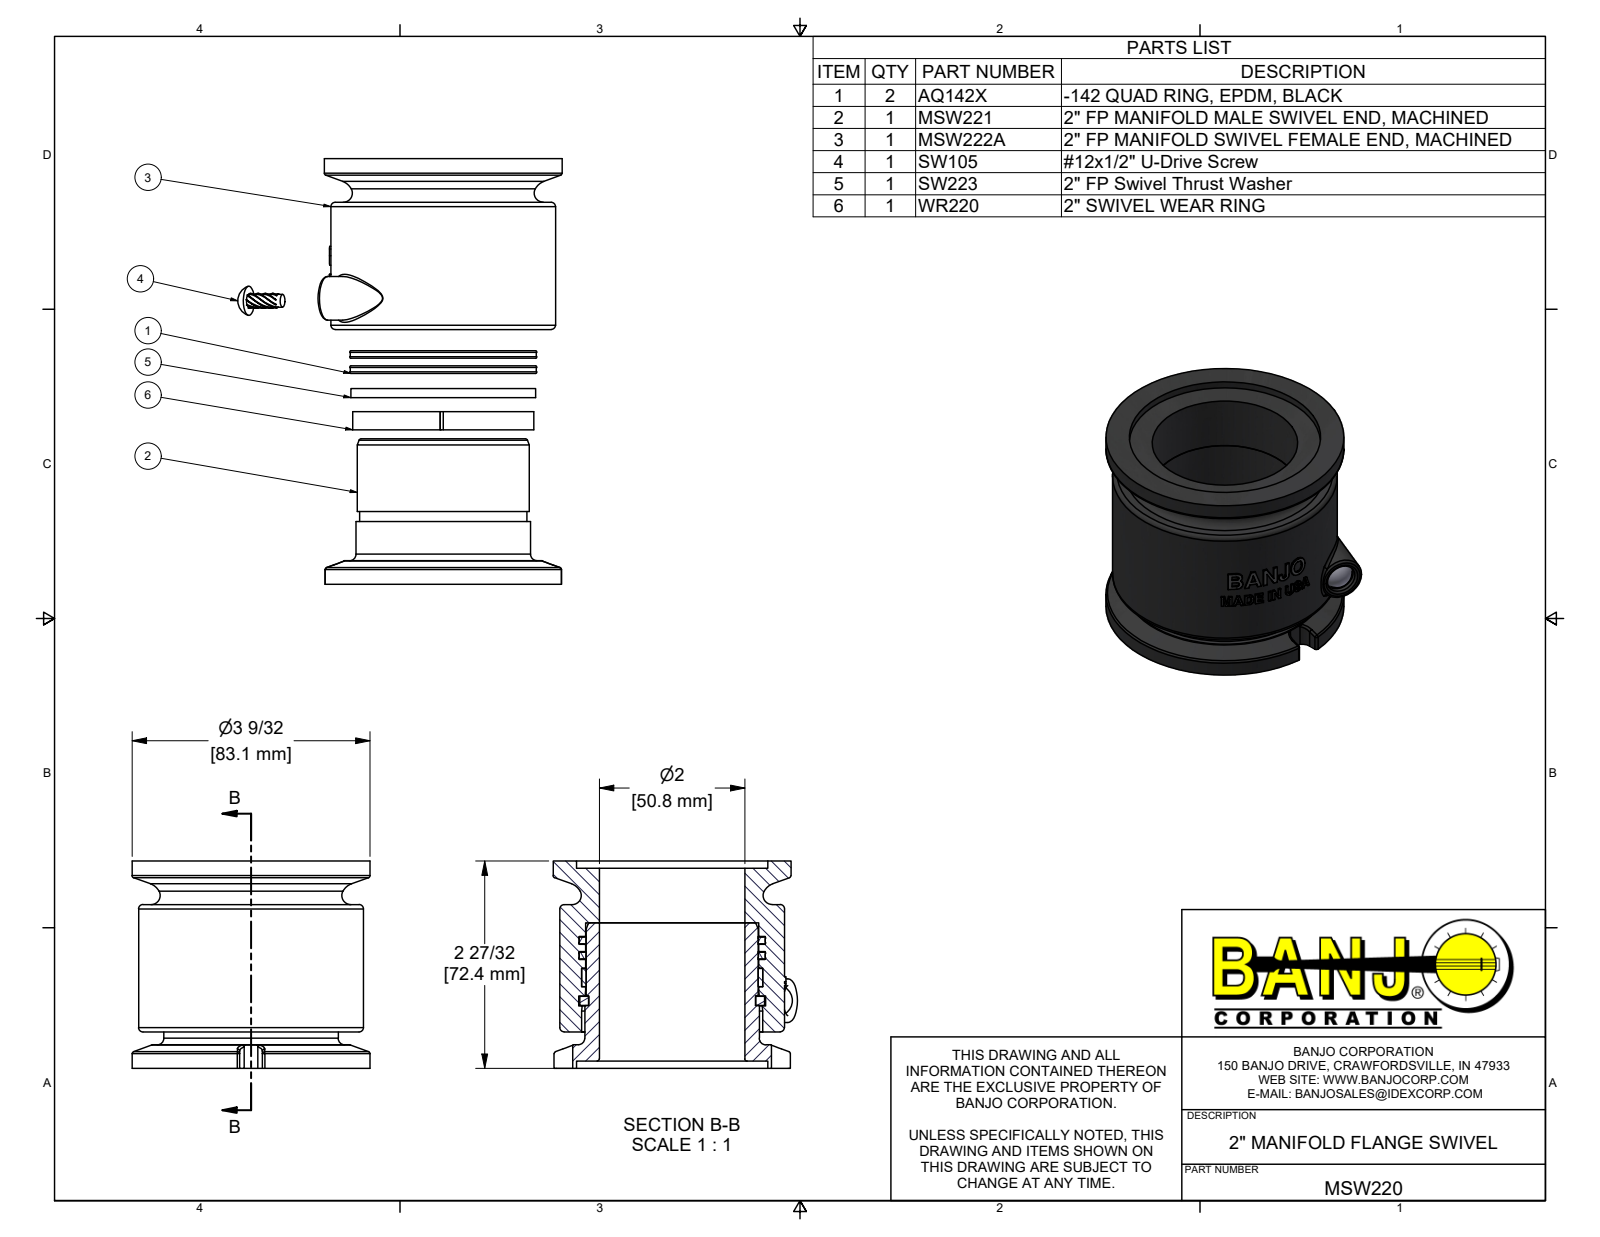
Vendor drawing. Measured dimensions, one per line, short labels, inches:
name: MSW220; MSW221; MSW221X; MSW222A (+5 more)
written by: Autodesk Inventor 2022 (AUTOMOTIVE_DESIGN)
unit: in
bodies: 7 solids, 349 faces (123 planar, 78 cylindrical, 148 other)
size: 3.357 × 3.27 × 2.85
volume: 10.91 in³; area: 111.8 in²
holes: 1× ⌀0.196, 1× ⌀0.21, 1× ⌀0.413, 1× ⌀2, 1× ⌀2.29, 1× ⌀2.364, 1× ⌀2.38, 1× ⌀2.489, 1× ⌀2.492, 1× ⌀2.558, 1× ⌀2.57, 1× ⌀2.63
bosses: 1× ⌀3.27, 1× ⌀3.09, 1× ⌀2.54, 1× ⌀2.4, 1× ⌀2.3, 1× ⌀0.202, 1× ⌀0.176
rounds: 8× R0.013, 4× R0.03, 2× R0.156, 1× R0.3, 1× R1.565
face distances: 0.1, 2.75, 0.5, 2.25, 2.85, 2, 0.75, 0.85, 1.9, 2.65
